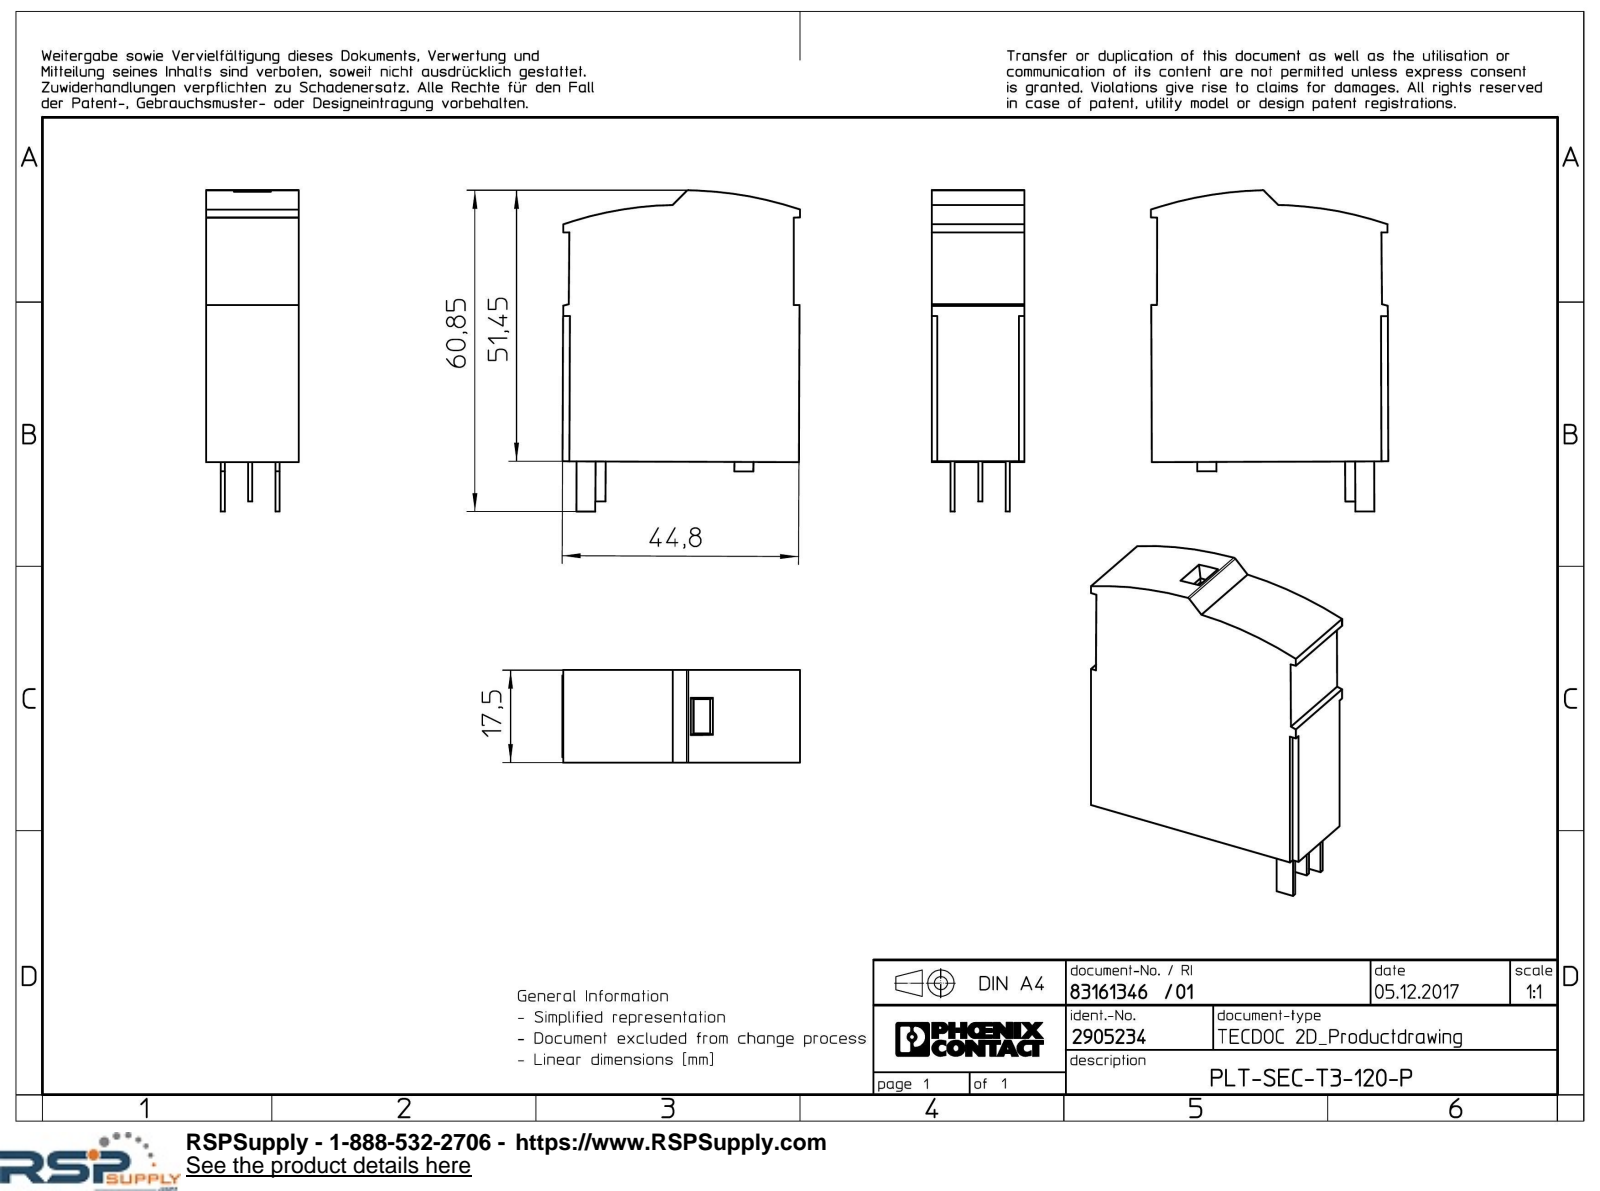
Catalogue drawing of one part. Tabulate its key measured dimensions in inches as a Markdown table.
| quantity | value |
| --- | --- |
| part name | PLT_SEC_T3_230_P-select |
| STEP written by | Creo Elements/Direct Modeling 20.1A 29-Sep-2018 (C) Parametric Technology GmbH (AUTOMOTIVE_DESIGN) |
| units | inches |
| bodies | 1 solid, 78 faces (74 planar, 3 cylindrical, 1 other) |
| overall size | 2.393 × 1.77 × 0.689 |
| volume | 2.133 in³ |
| surface area | 13.64 in² |
| partial cylindrical surfaces (radius × count) | 0.02 × 1, 2.717 × 1, 2.827 × 1 |
| main face-to-face distances | 0.689, 1.763, 0.028, 0.661, 0.205, 0.031, 0.039, 0.634, 0.14, 0.549 |
